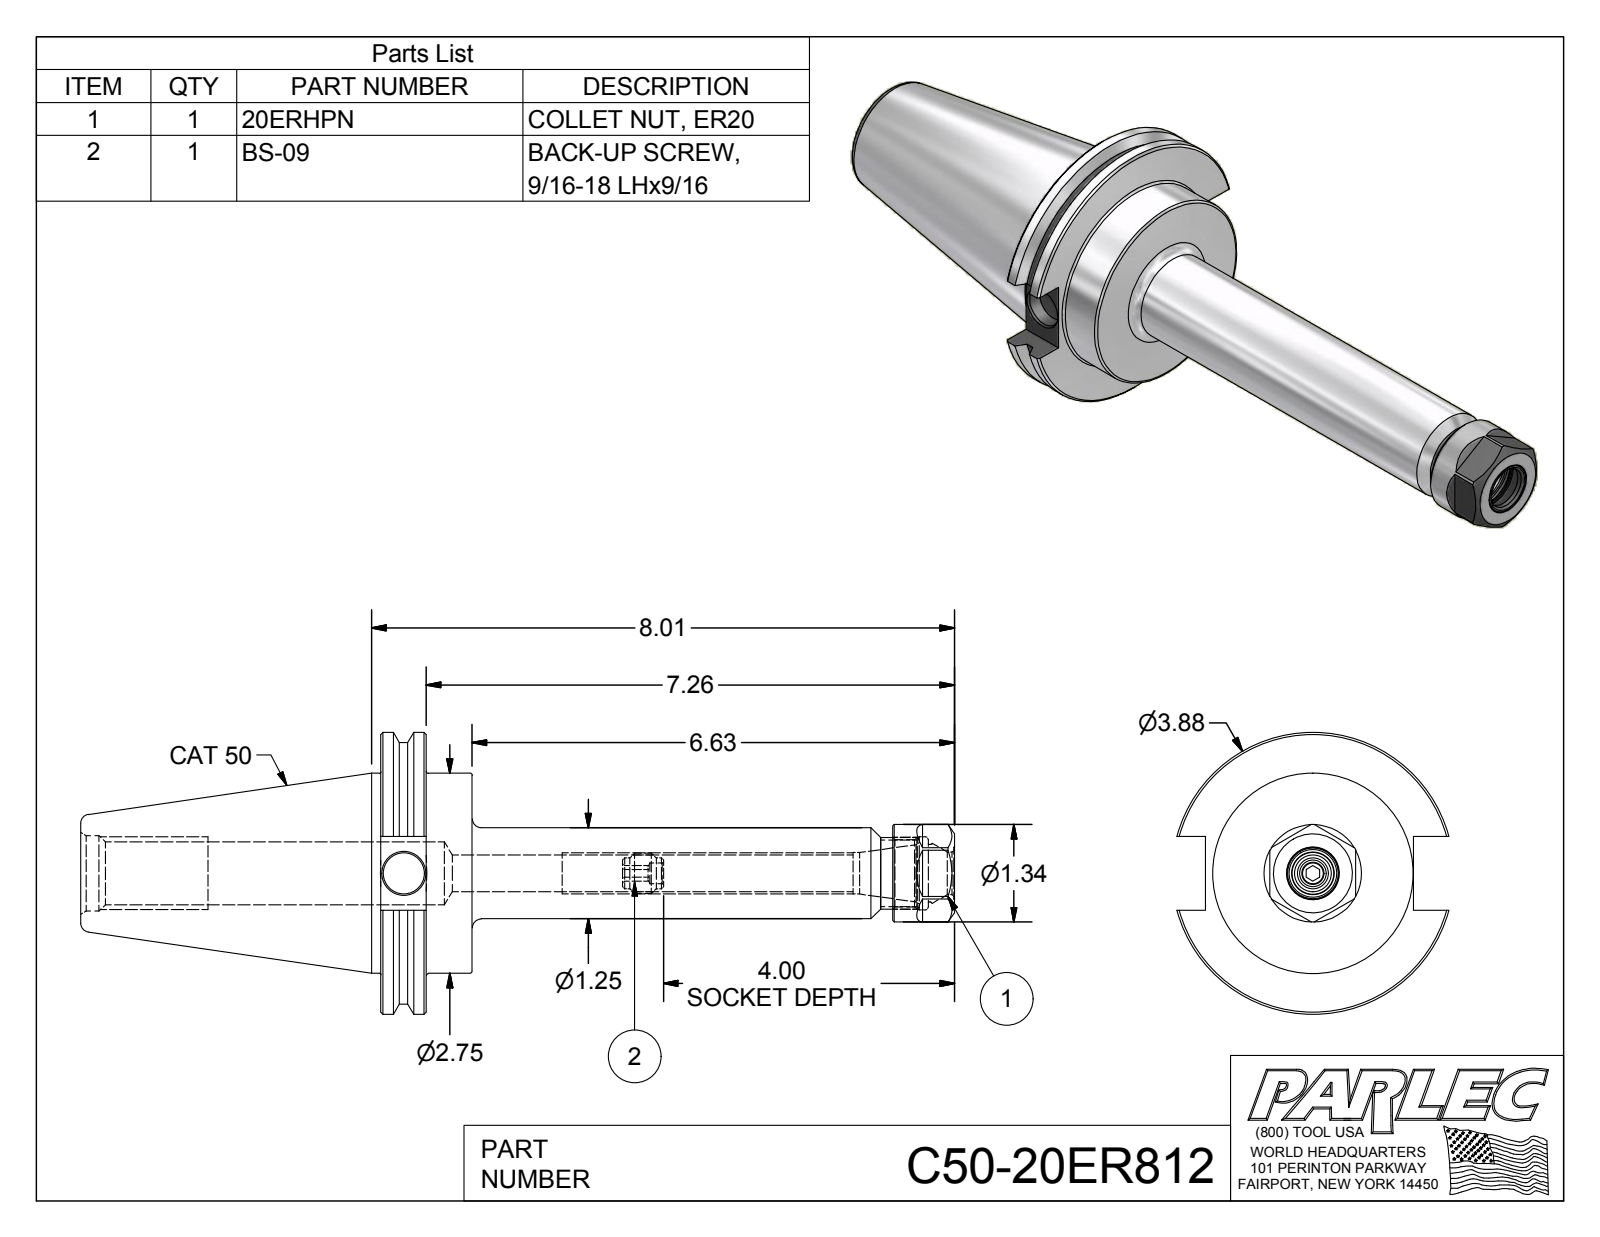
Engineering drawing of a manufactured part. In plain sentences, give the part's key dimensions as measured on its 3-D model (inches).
The part is named "C50-20ER812; C50-20ER8-1; 20ERHPN; BS-09". Its 3-D file was written by "Autodesk Inventor 2012 (AUTOMOTIVE_DESIGN)". It is 3 solids with 107 faces: 42 planar, 24 cylindrical and 41 other. Overall it measures 12.012 by 3.875 by 3.74 inches. Its volume is 29.48 cubic inches and its surface area 116.9 square inches. Round holes: 1 of diameter 0.281, 1 of diameter 0.502, 1 of diameter 0.563, 1 of diameter 0.57, 1 of diameter 0.587, 1 of diameter 0.79, 1 of diameter 0.865, 1 of diameter 0.926, 1 of diameter 1.005, 1 of diameter 1.038. Round bosses or shafts: 1 of diameter 3.875, 1 of diameter 3.594, 1 of diameter 2.75, 1 of diameter 1.34, 1 of diameter 1.25, 1 of diameter 0.984, 1 of diameter 0.555, 1 of diameter 0.422. The main face-to-face distances are 0.625, 1.255, 0.63, 1.18, 7.036, 6.411, 5.781, 7.886, 7.261, 6.631.
